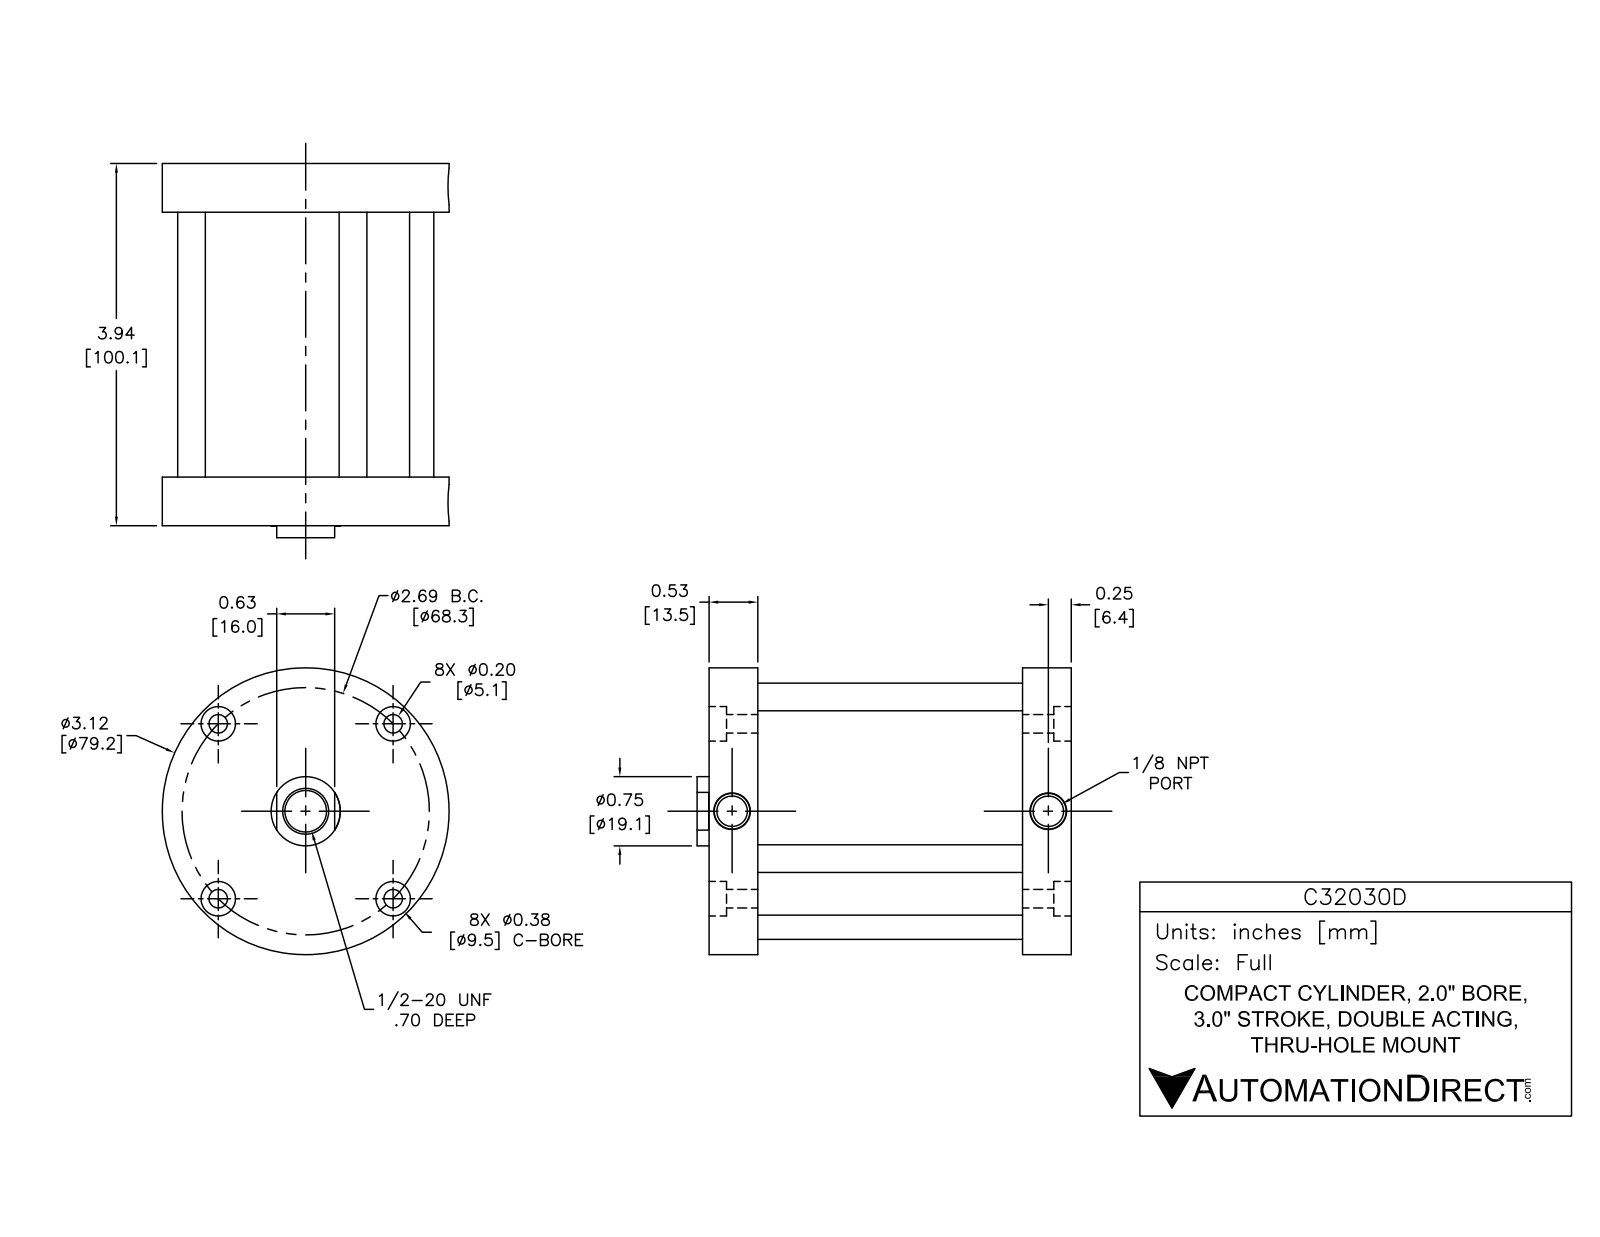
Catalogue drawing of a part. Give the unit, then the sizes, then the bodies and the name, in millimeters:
Units: millimetres
Overall size (bounding box): 103.4 × 79.2 × 79.2
Round holes (diameter × count): ⌀5.1 ×4, ⌀5.5 ×4, ⌀8.7 ×4, ⌀3.2 ×2, ⌀11.3 ×1, ⌀19.1 ×1, ⌀19.1 ×1, ⌀50.8 ×1, ⌀52.3 ×1
Round bosses / shafts (diameter × count): ⌀10.2 ×4, ⌀79.2 ×1
Main face-to-face distances: 79.5, 6.4, 7.1, 100.1, 93, 86.6, 86.6, 13.5, 13.5, 73.2
Hole centre spacings: 11, 34.2, 34.2, 39.9, 48.3, 48.3, 55.4, 67.4
Volume: 174 700 mm³ · Surface area: 83 030 mm²
Bodies: 9 solids, 165 faces (49 planar, 98 cylindrical, 18 other)
Part name (STEP PRODUCT): C32030D-FO1_BM_rod; C32030D; C32030D-FO1_BM_tube; C32030D-FO1_BM_heads (+3 more)
STEP written by: SolidWorks 2014 (AUTOMOTIVE_DESIGN)
